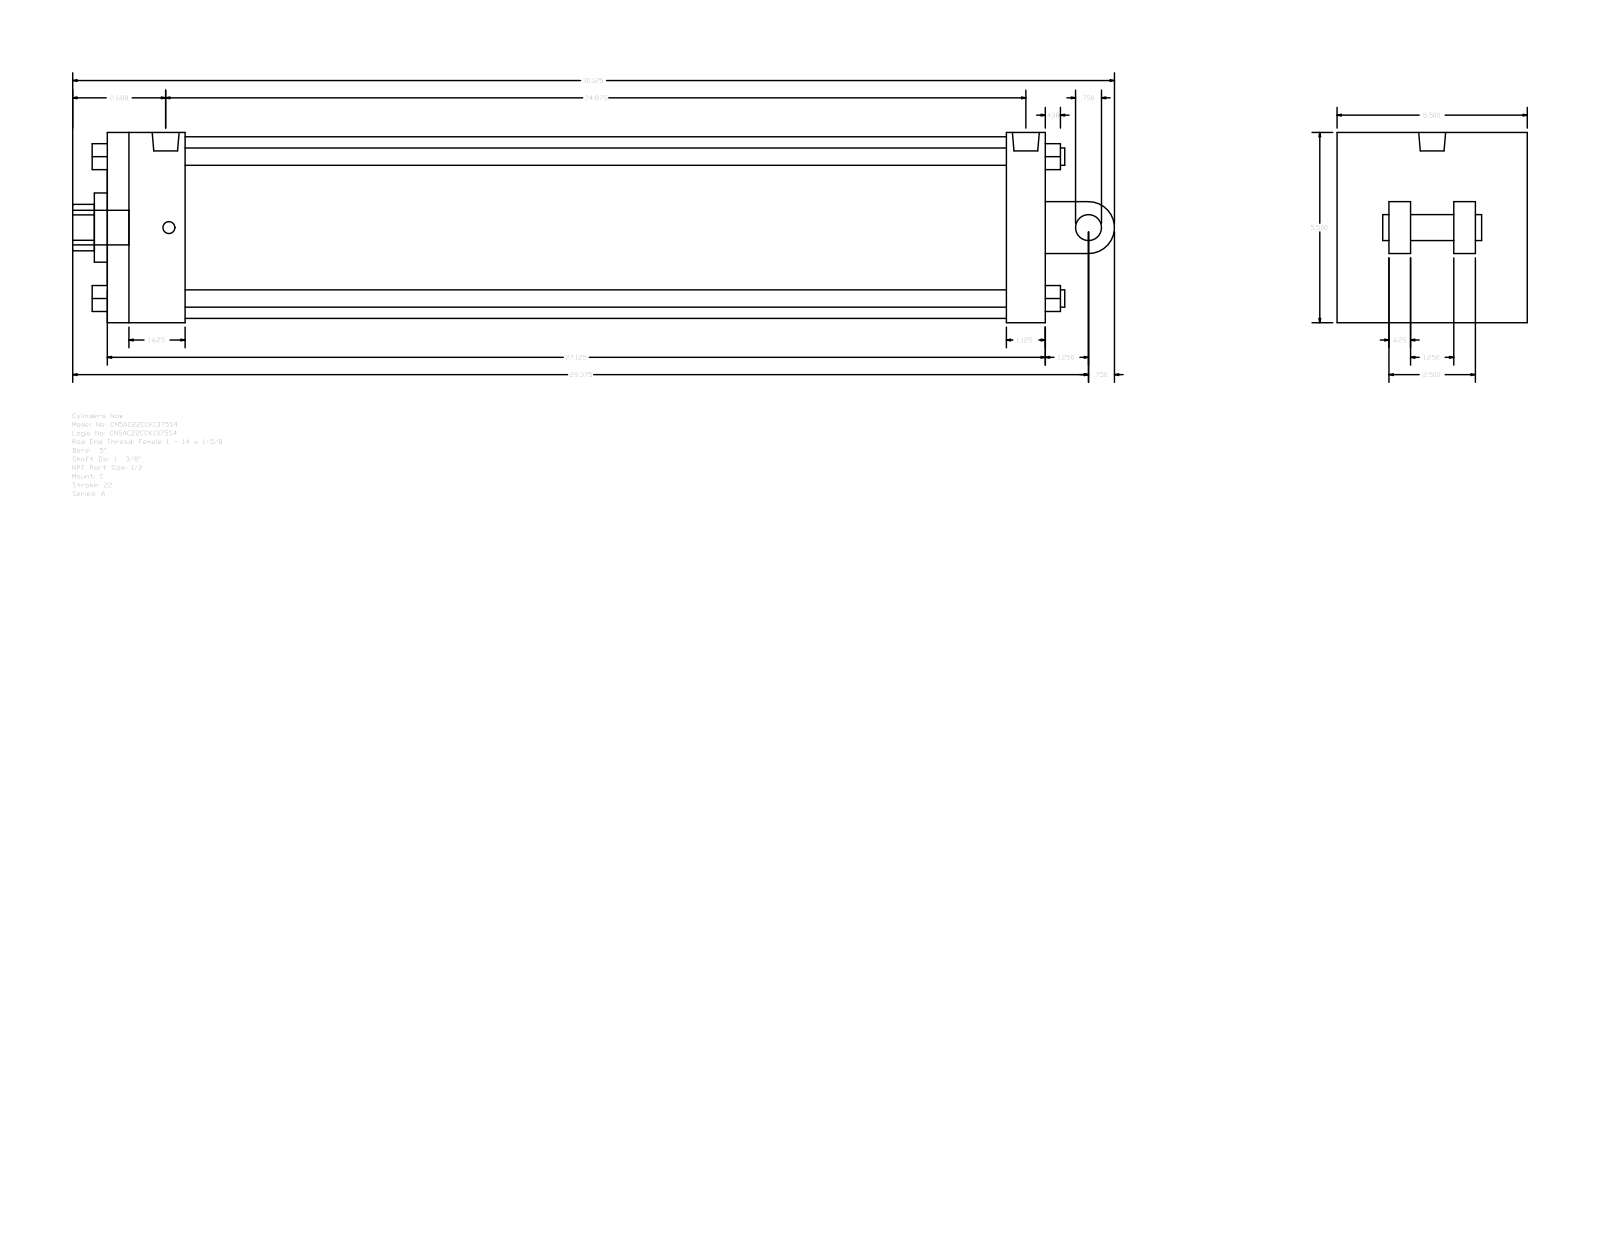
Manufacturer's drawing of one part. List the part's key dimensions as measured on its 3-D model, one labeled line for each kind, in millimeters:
Part name (STEP PRODUCT): A_C__0500_1.375
STEP written by: GSSL Pune (CONFIG_CONTROL_DESIGN)
Units: millimetres
Bodies: 0 solids, 135 faces (102 planar, 33 cylindrical, 0 other)
Overall size (bounding box): 765.17 × 139.7 × 139.7
Round holes (diameter × count): ⌀8.73 ×2, ⌀19.77 ×1, ⌀34.92 ×1, ⌀50.8 ×1, ⌀133.35 ×1
Round bosses / shafts (diameter × count): ⌀12.7 ×4, ⌀8.73 ×2, ⌀25.4 ×1, ⌀19.77 ×1, ⌀19.05 ×1
Partial cylindrical surfaces — rounded edges, fillets, slot ends (radius × count): R17.06 ×1, R19.05 ×1
Main face-to-face distances: 139.7, 688.98, 28.58, 57.15, 660.4, 603.25, 631.83, 38.1, 15.87, 53.97
Hole centre spacings: 2.39
